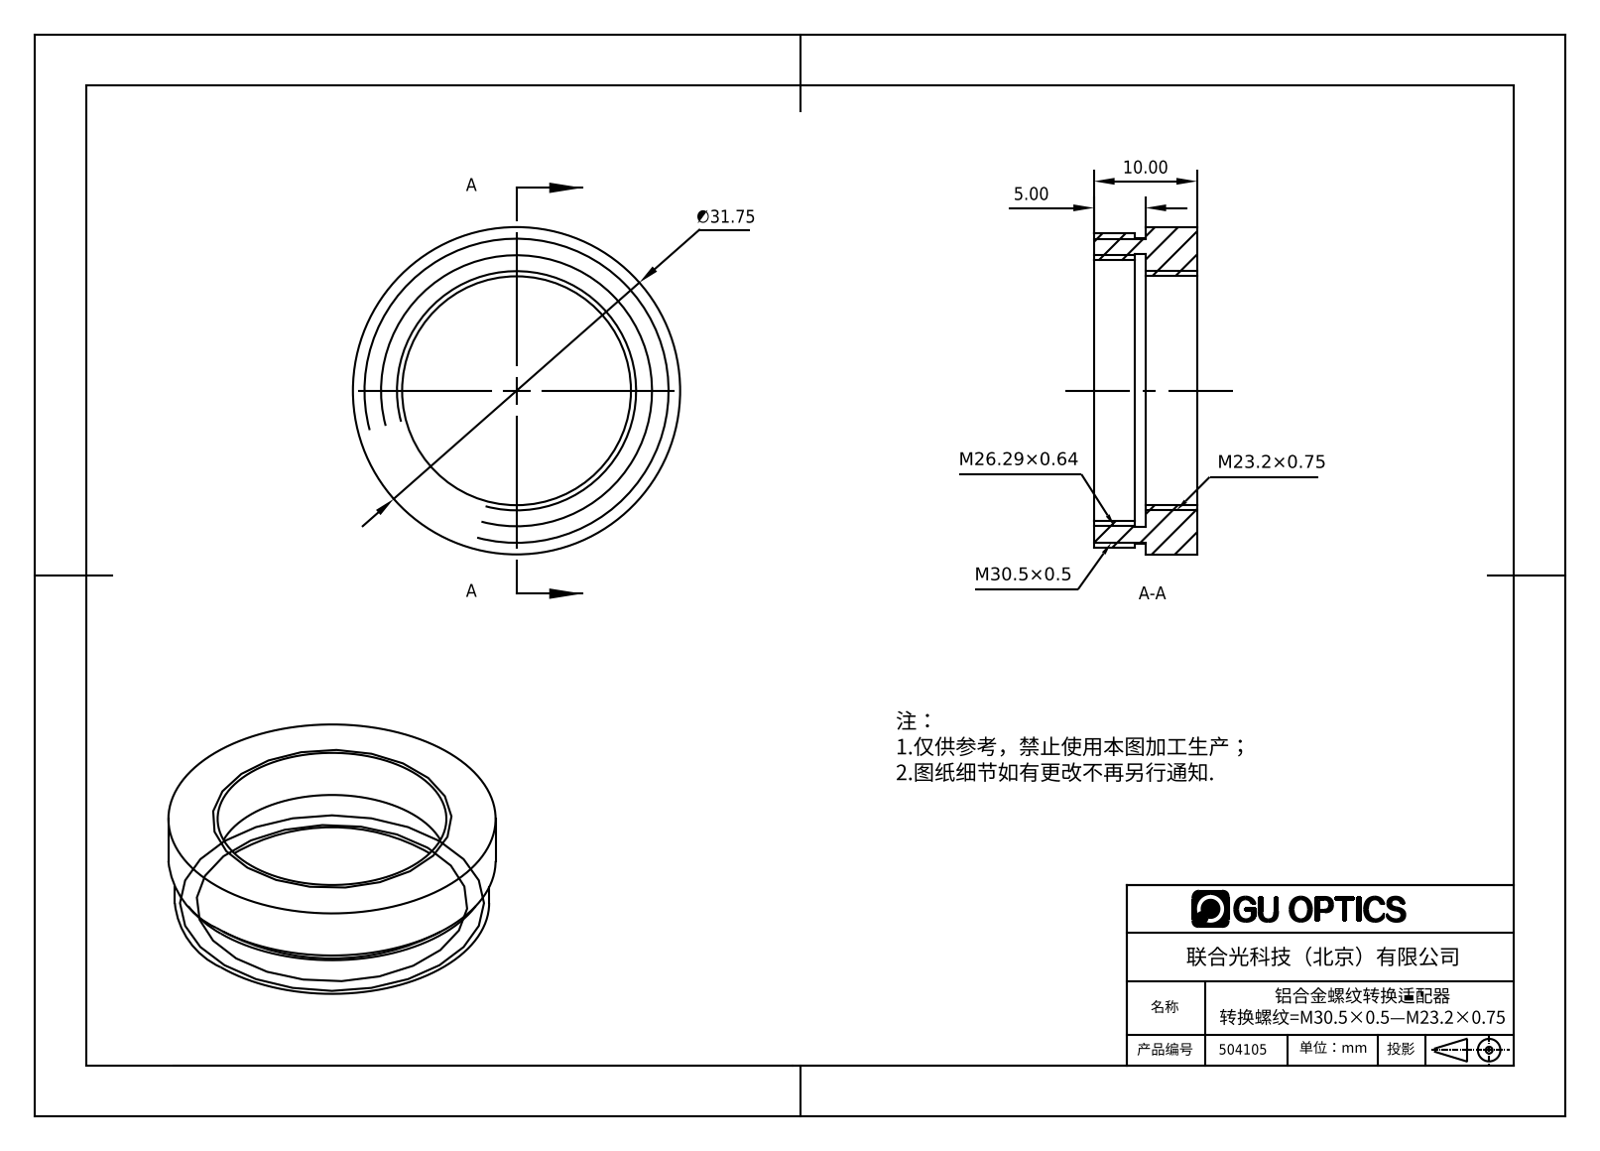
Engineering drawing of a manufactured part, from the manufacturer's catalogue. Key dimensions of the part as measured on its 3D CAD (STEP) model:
Part name (STEP PRODUCT): 504105
STEP written by: SolidWorks 2016 (AUTOMOTIVE_DESIGN)
Units: millimetres
Bodies: 1 solid, 18 faces (6 planar, 12 cylindrical, 0 other)
Overall size (bounding box): 31.75 × 31.75 × 10
Volume: 3 078 mm³ · Surface area: 2 708 mm²
Round holes (diameter × count): ⌀22.2 ×1, ⌀25.29 ×1, ⌀26.5 ×1
Round bosses / shafts (diameter × count): ⌀31.75 ×1, ⌀30.5 ×1, ⌀29.7 ×1
Main face-to-face distances: 5, 10, 4, 1, 6
